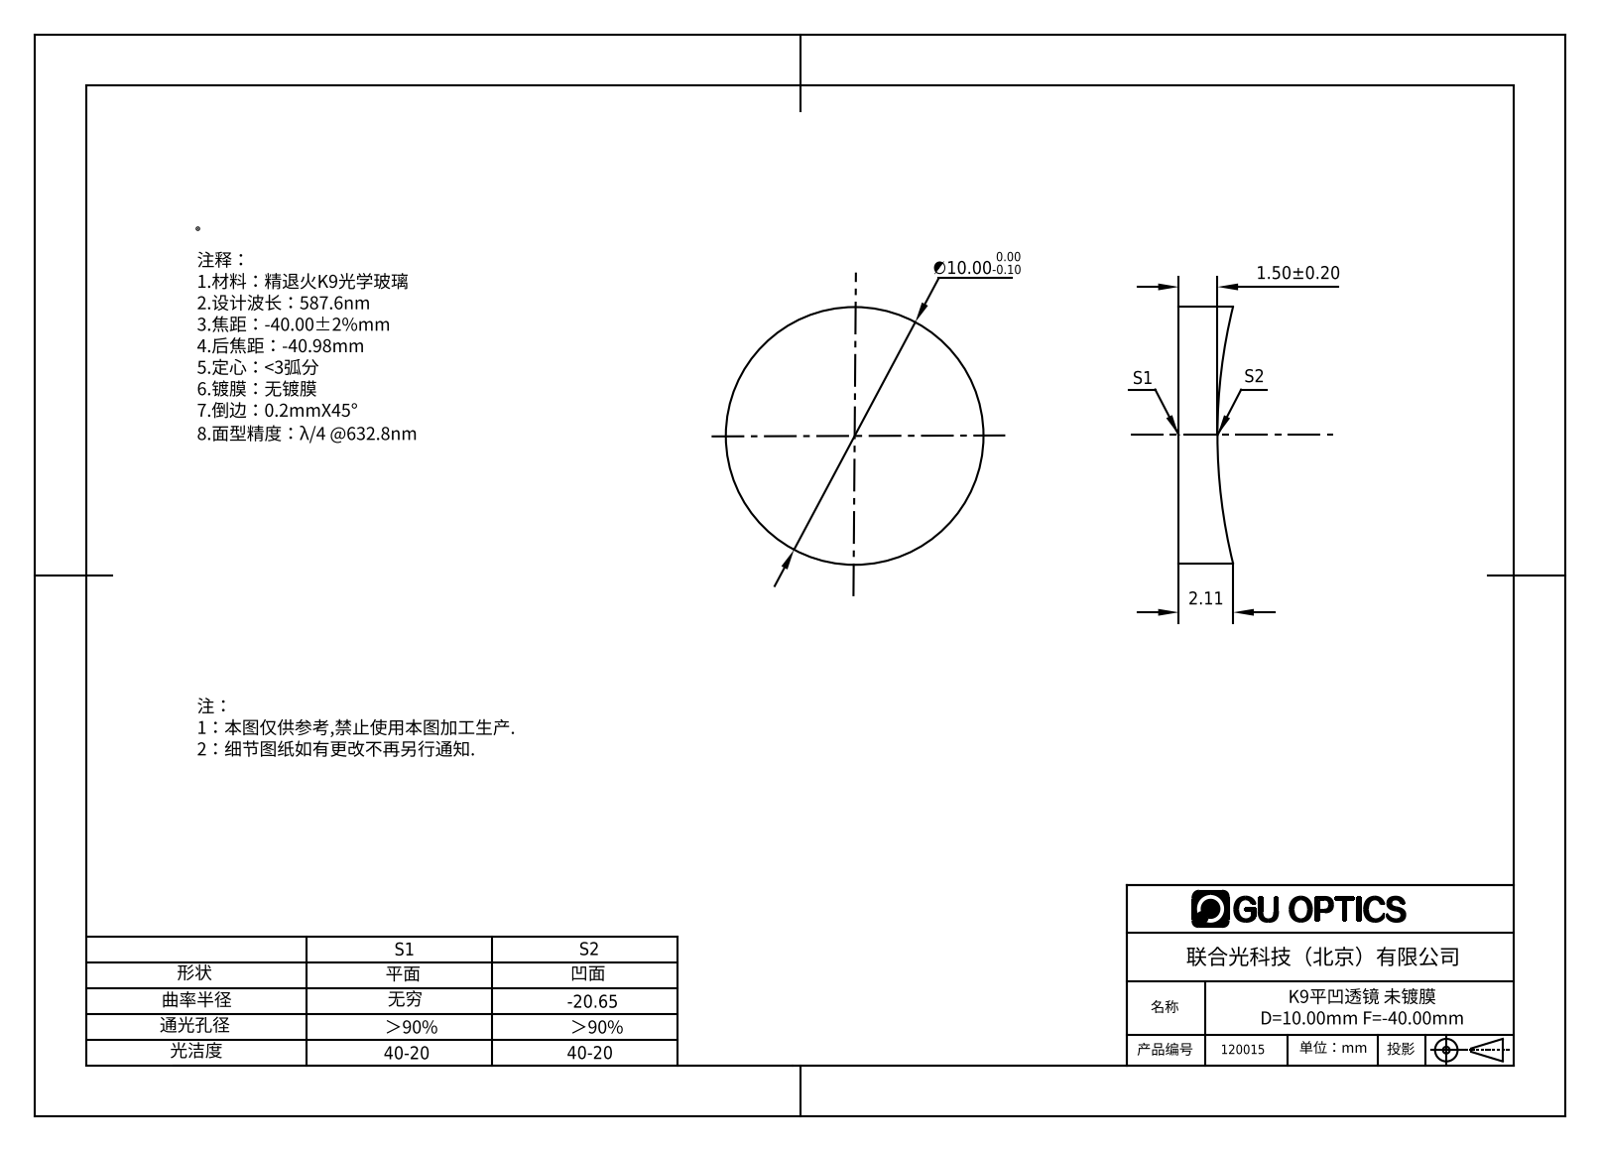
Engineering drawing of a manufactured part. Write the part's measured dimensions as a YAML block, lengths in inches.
part_name: "120015"
step_written_by: "SolidWorks 2016 (AUTOMOTIVE_DESIGN)"
units: inches
bodies: {solids: 1, faces: 5, planar: 1, cylindrical: 2, other: 2}
overall_size: [0.394, 0.394, 0.083]
volume: 0.009
surface_area: 0.349
round_bosses_or_shafts:
  - {diameter: 0.394, count: 1}
